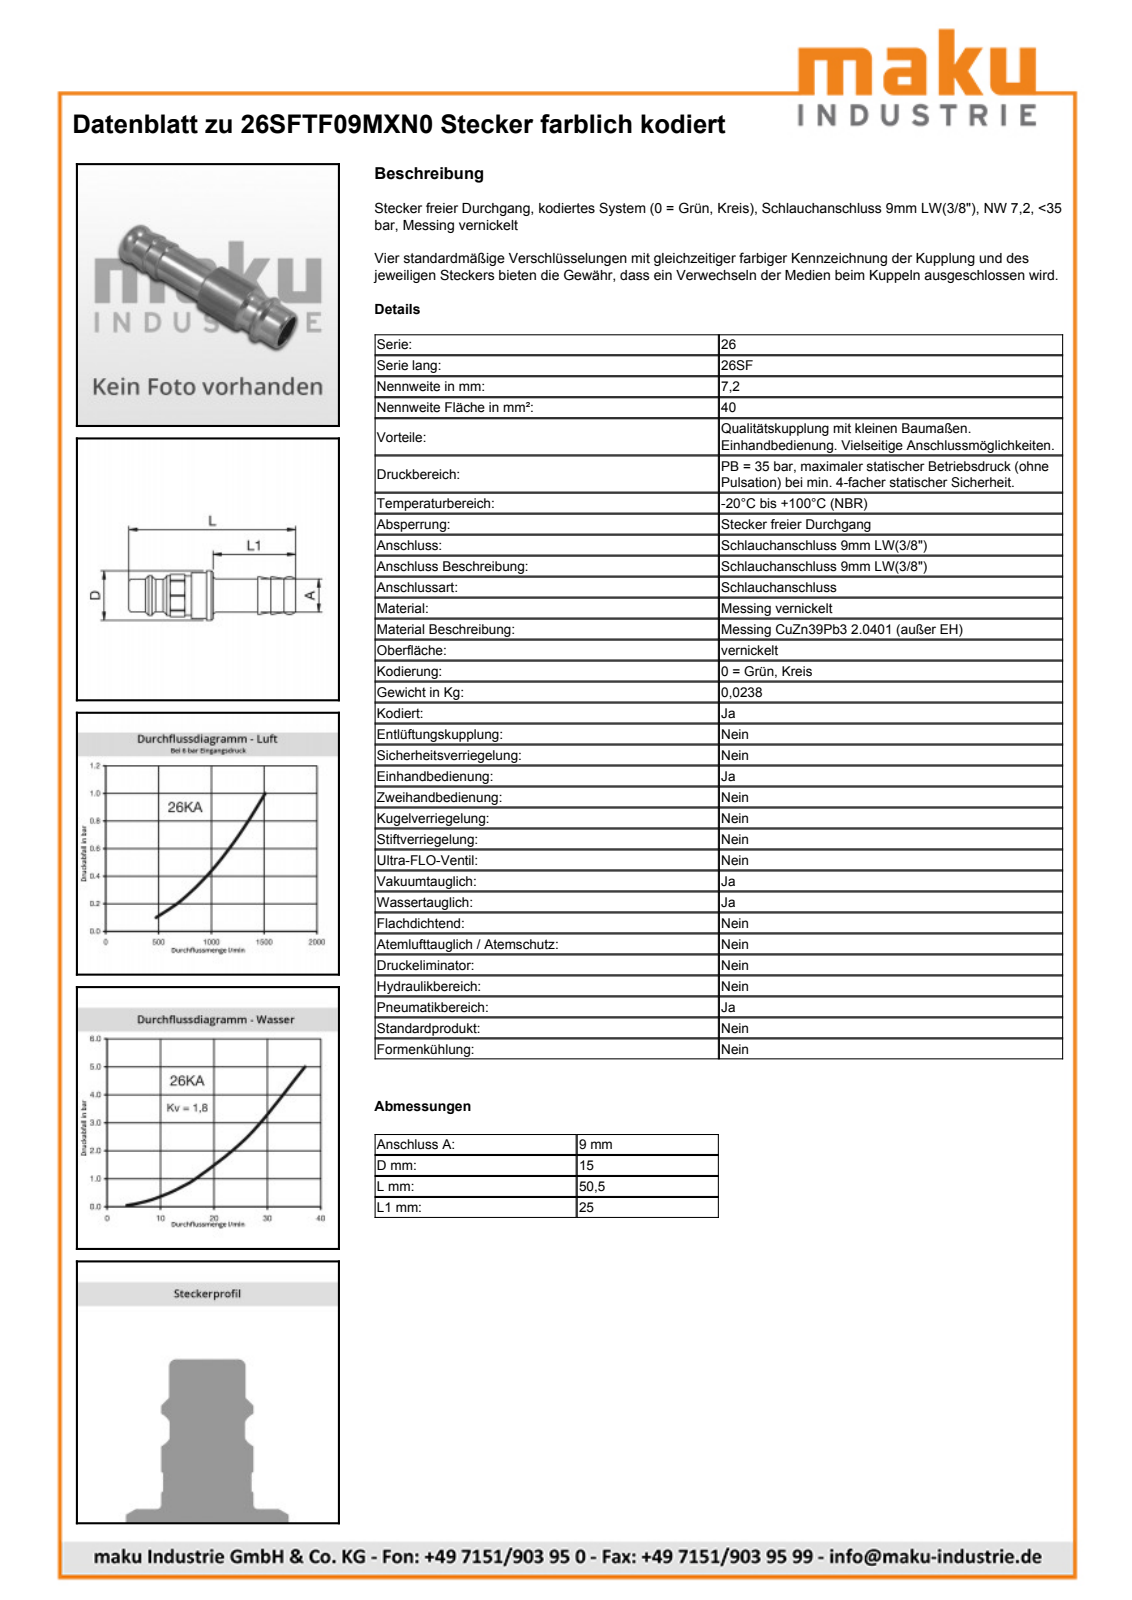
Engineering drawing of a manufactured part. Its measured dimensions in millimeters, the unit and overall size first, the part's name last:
Units: millimetres
Overall size (bounding box): 50.5 × 15.5 × 15.5
Round holes (diameter × count): ⌀7 ×1, ⌀13.85 ×1, ⌀14.05 ×1
Round bosses / shafts (diameter × count): ⌀15.5 ×1, ⌀15 ×1, ⌀14 ×1, ⌀12.5 ×1, ⌀12 ×1, ⌀10 ×1, ⌀9.75 ×1, ⌀9.1 ×1
Main face-to-face distances: 2, 6.2, 4.2, 6.5, 4.5, 25, 27, 31.2, 31.5, 11.5
Volume: 2 885 mm³ · Surface area: 3 539 mm²
Bodies: 2 solids, 37 faces (8 planar, 12 cylindrical, 17 other)
Part name (STEP PRODUCT): D106590; D106040; D103012
STEP written by: Autodesk Inventor 2011 (AUTOMOTIVE_DESIGN)
